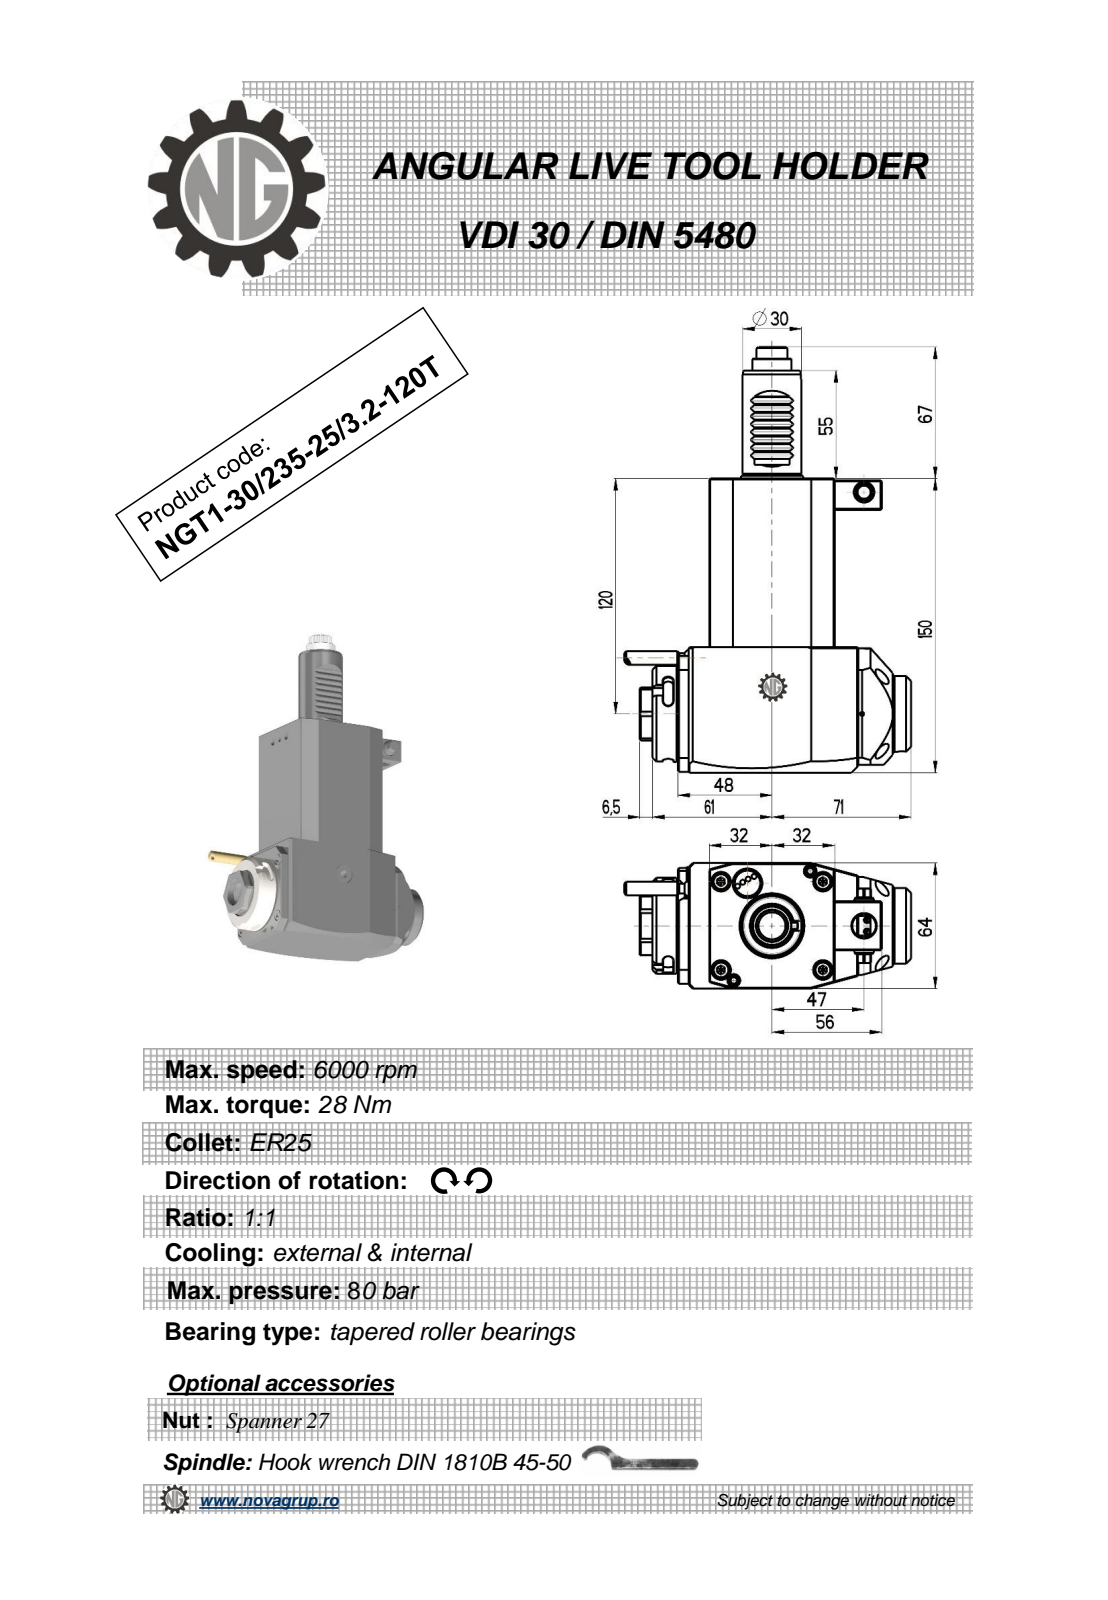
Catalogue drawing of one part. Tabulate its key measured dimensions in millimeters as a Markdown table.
| quantity | value |
| --- | --- |
| part name | NGT1_30_235_25_3_2_120T |
| STEP written by | PRO/ENGINEER BY PARAMETRIC TECHNOLOGY CORPORATION, 2010280 (CONFIG_CONTROL_DESIGN) |
| units | millimeters |
| bodies | 1 solid, 433 faces (188 planar, 155 cylindrical, 90 other) |
| overall size | 217 × 146.38 × 64 |
| volume | 831 171 mm³ |
| surface area | 67 805 mm² |
| round holes (diameter × count) | 2.5 × 1, 3 × 1, 9.5 × 1, 12 × 1, 18 × 1 |
| round bosses / shafts (diameter × count) | 8 × 2, 49 × 1, 42 × 1, 38.5 × 1, 30 × 1, 20 × 1, 10 × 1, 7 × 1 |
| partial cylindrical surfaces (radius × count) | 1.98 × 36, 0.3 × 8, 2.5 × 6, 180 × 2, 3.85 × 1, 4.25 × 1, 4.5 × 1, 7.08 × 1 |
| main face-to-face distances | 64, 150, 16, 72.18, 80, 13, 86, 93, 29, 103 |
| hole center spacings | 34.25, 85.15, 111.5 |
